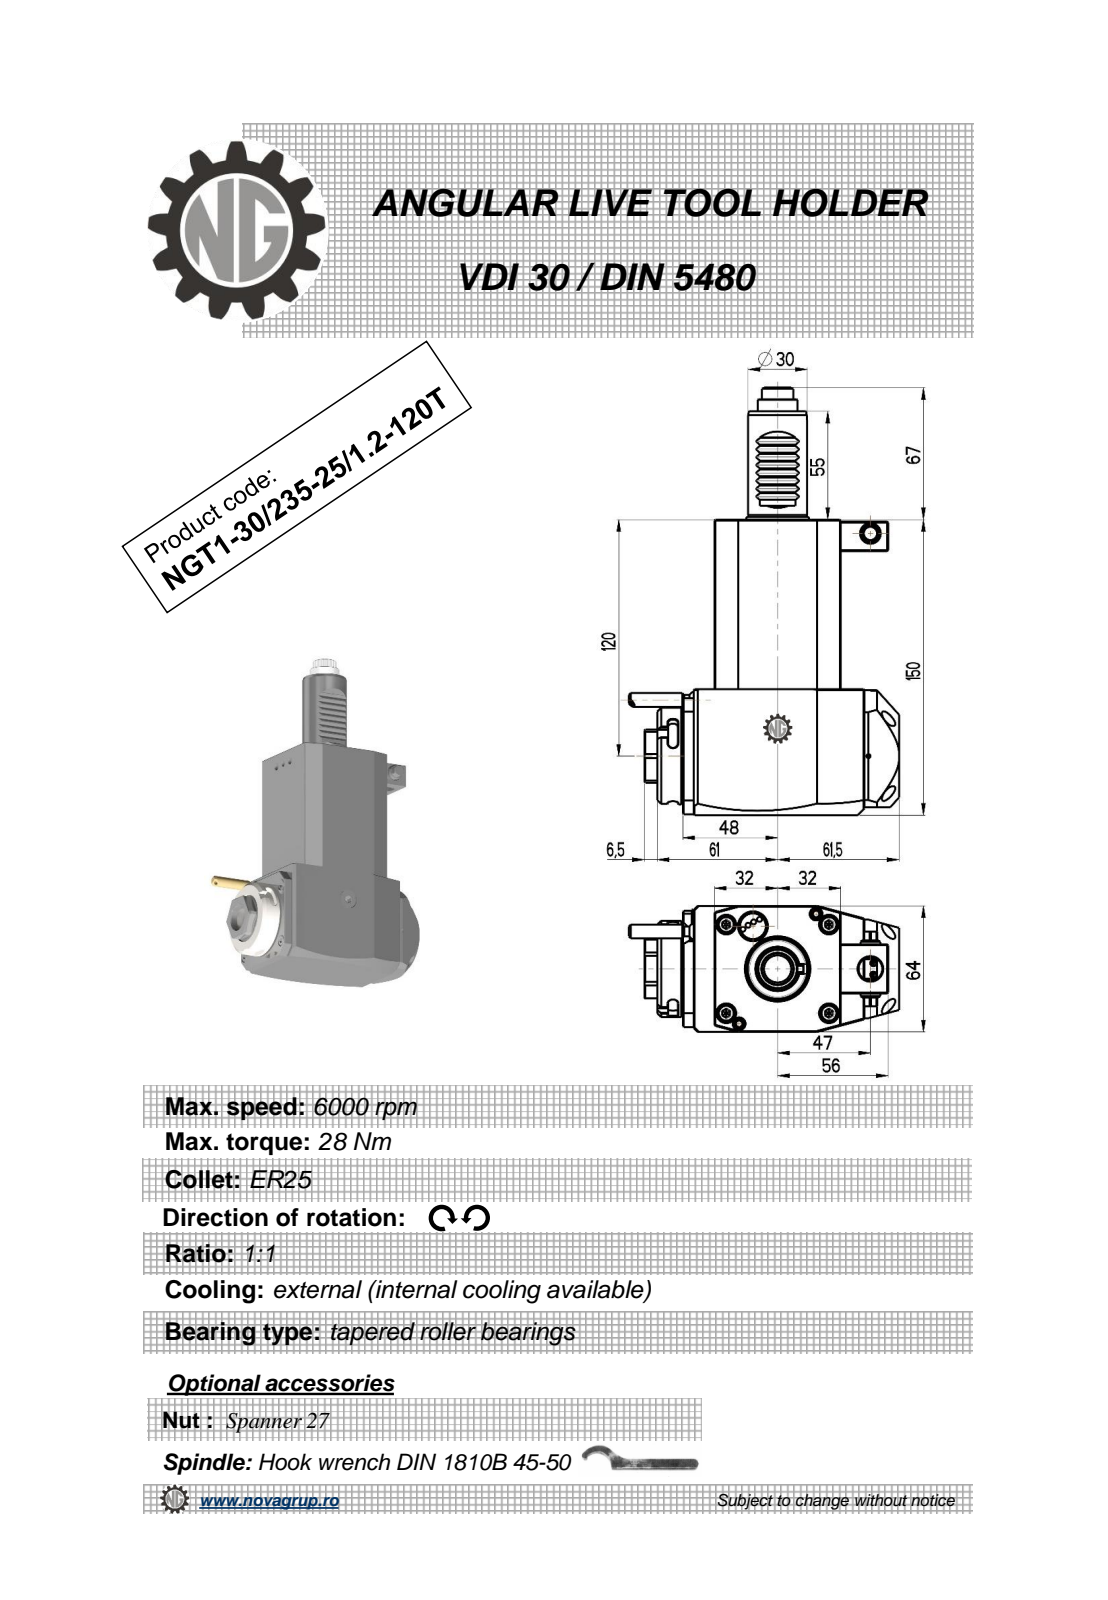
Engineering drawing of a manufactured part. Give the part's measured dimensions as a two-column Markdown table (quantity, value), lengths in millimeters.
| quantity | value |
| --- | --- |
| part name | NGT1_30_235_25_1_2_120T |
| STEP written by | PRO/ENGINEER BY PARAMETRIC TECHNOLOGY CORPORATION, 2010280 (CONFIG_CONTROL_DESIGN) |
| units | millimeters |
| bodies | 1 solid, 427 faces (186 planar, 153 cylindrical, 88 other) |
| overall size | 217 × 136.88 × 64 |
| volume | 820 301 mm³ |
| surface area | 66 953 mm² |
| round holes (diameter × count) | 2.5 × 1, 3 × 1, 9.5 × 1, 12 × 1, 18 × 1 |
| round bosses / shafts (diameter × count) | 8 × 2, 49 × 1, 42 × 1, 30 × 1, 20 × 1, 10 × 1, 7 × 1, 5 × 1 |
| partial cylindrical surfaces (radius × count) | 1.98 × 36, 0.3 × 8, 2.5 × 6, 180 × 2, 3.85 × 1, 4.25 × 1, 4.5 × 1, 7.08 × 1 |
| main face-to-face distances | 64, 150, 16, 72.18, 80, 13, 29.5, 86, 109.5, 93.5 |
| hole center spacings | 34.25, 85.15, 111.5 |
